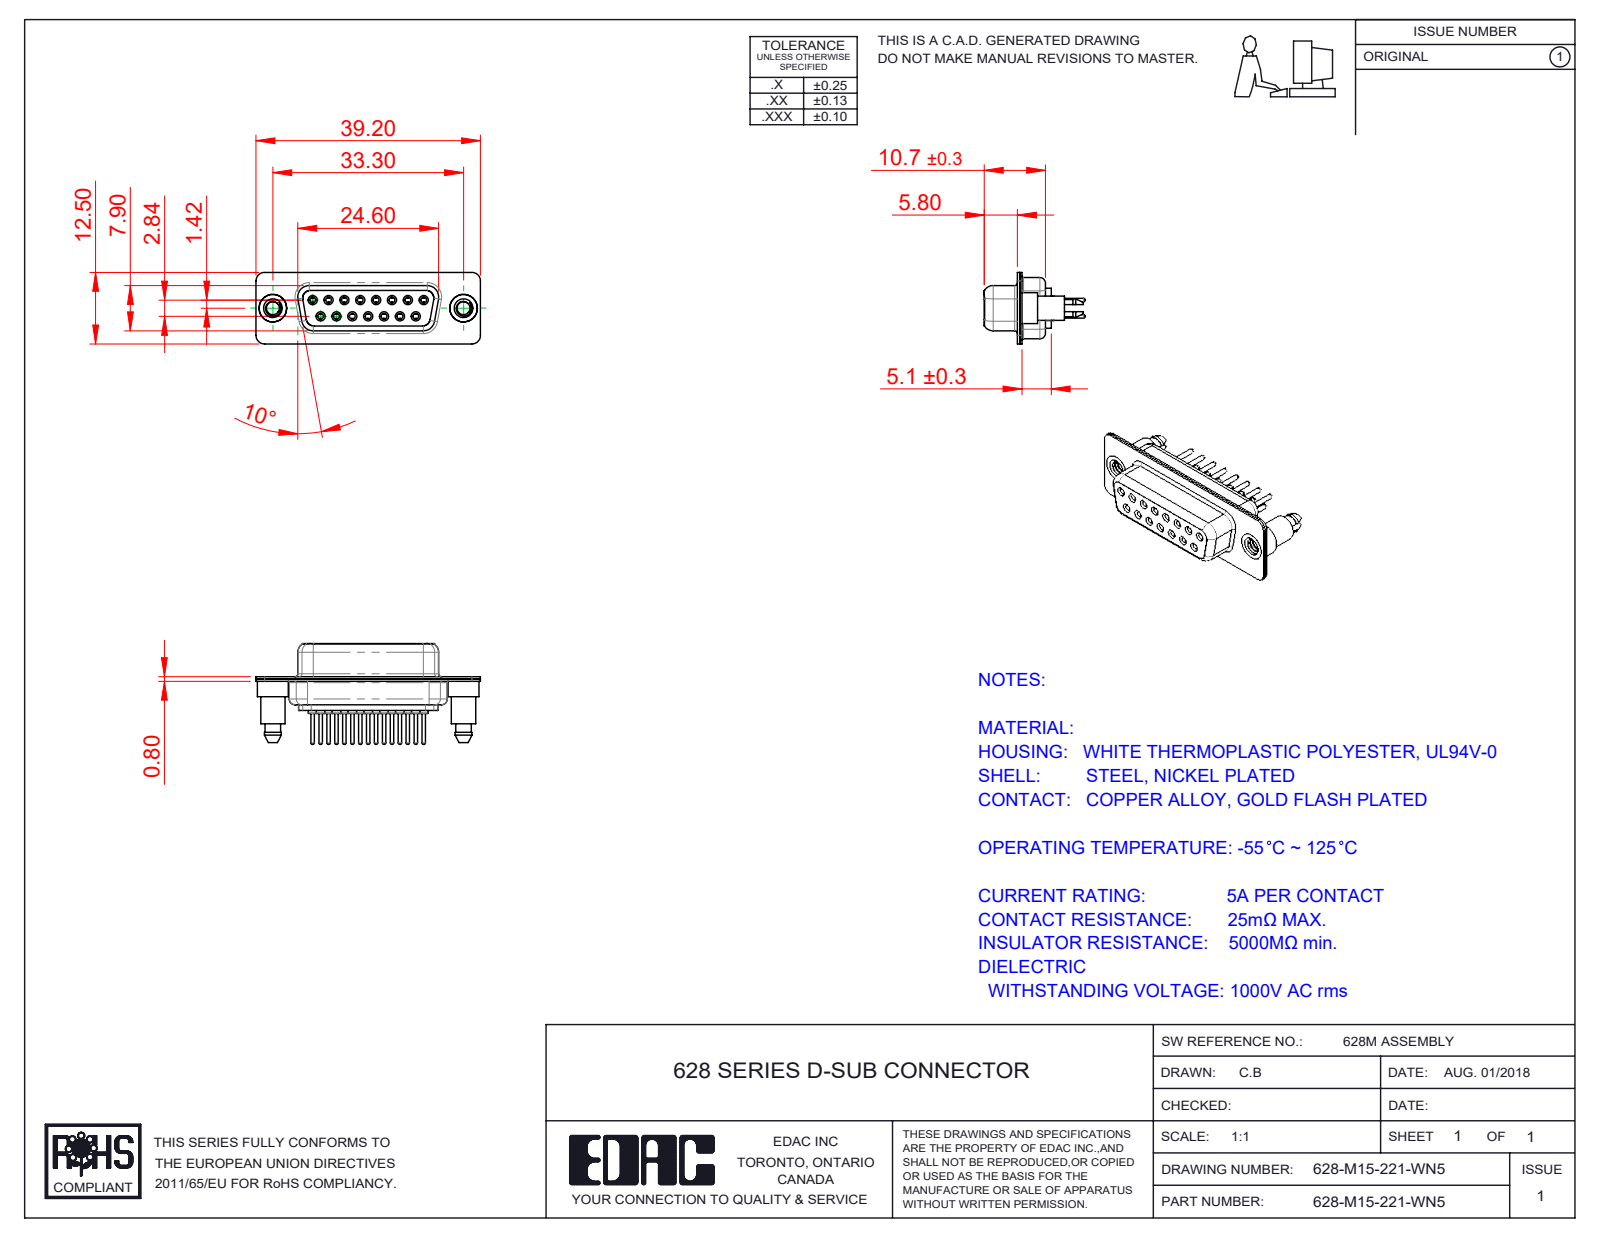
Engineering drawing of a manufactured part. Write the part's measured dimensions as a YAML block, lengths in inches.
part_name: "628M Shell Front_15 Contacts; 628-M15-221-WN5; 628M Shell Rear_15 Contacts; 628M Housing_15 Contacts (+3 more)"
step_written_by: "SolidWorks 2020 (CONFIG_CONTROL_DESIGN)"
units: inches
bodies: {solids: 20, faces: 1154, planar: 308, cylindrical: 454, other: 392}
overall_size: [1.543, 0.693, 0.492]
volume: 0.159
surface_area: 10.13
round_holes:
  - {diameter: 0.039, count: 15}
  - {diameter: 0.043, count: 15}
  - {diameter: 0.067, count: 15}
  - {diameter: 0.071, count: 15}
  - {diameter: 0.079, count: 15}
  - {diameter: 0.089, count: 2}
  - {diameter: 0.157, count: 2}
  - {diameter: 0.189, count: 2}
round_bosses_or_shafts:
  - {diameter: 0.087, count: 15}
  - {diameter: 0.063, count: 15}
  - {diameter: 0.059, count: 15}
  - {diameter: 0.024, count: 15}
  - {diameter: 0.213, count: 2}
  - {diameter: 0.193, count: 2}
  - {diameter: 0.167, count: 2}
partial_cylinders:
  - {radius: 0.059, count: 18}
  - {radius: 0.079, count: 12}
  - {radius: 0.063, count: 10}
  - {radius: 0.053, count: 8}
  - {radius: 0.01, count: 4}
  - {radius: 0.02, count: 4}
  - {radius: 0.024, count: 4}
  - {radius: 0.026, count: 4}
face_to_face_distances: [0.016, 0.055, 0.018, 0.333, 0.071, 0.35, 0.244, 0.039, 0.278, 0.073]
hole_center_spacings: [0.124, 0.109, 0.218, 0.327, 0.436, 0.198, 0.198, 0.294]
